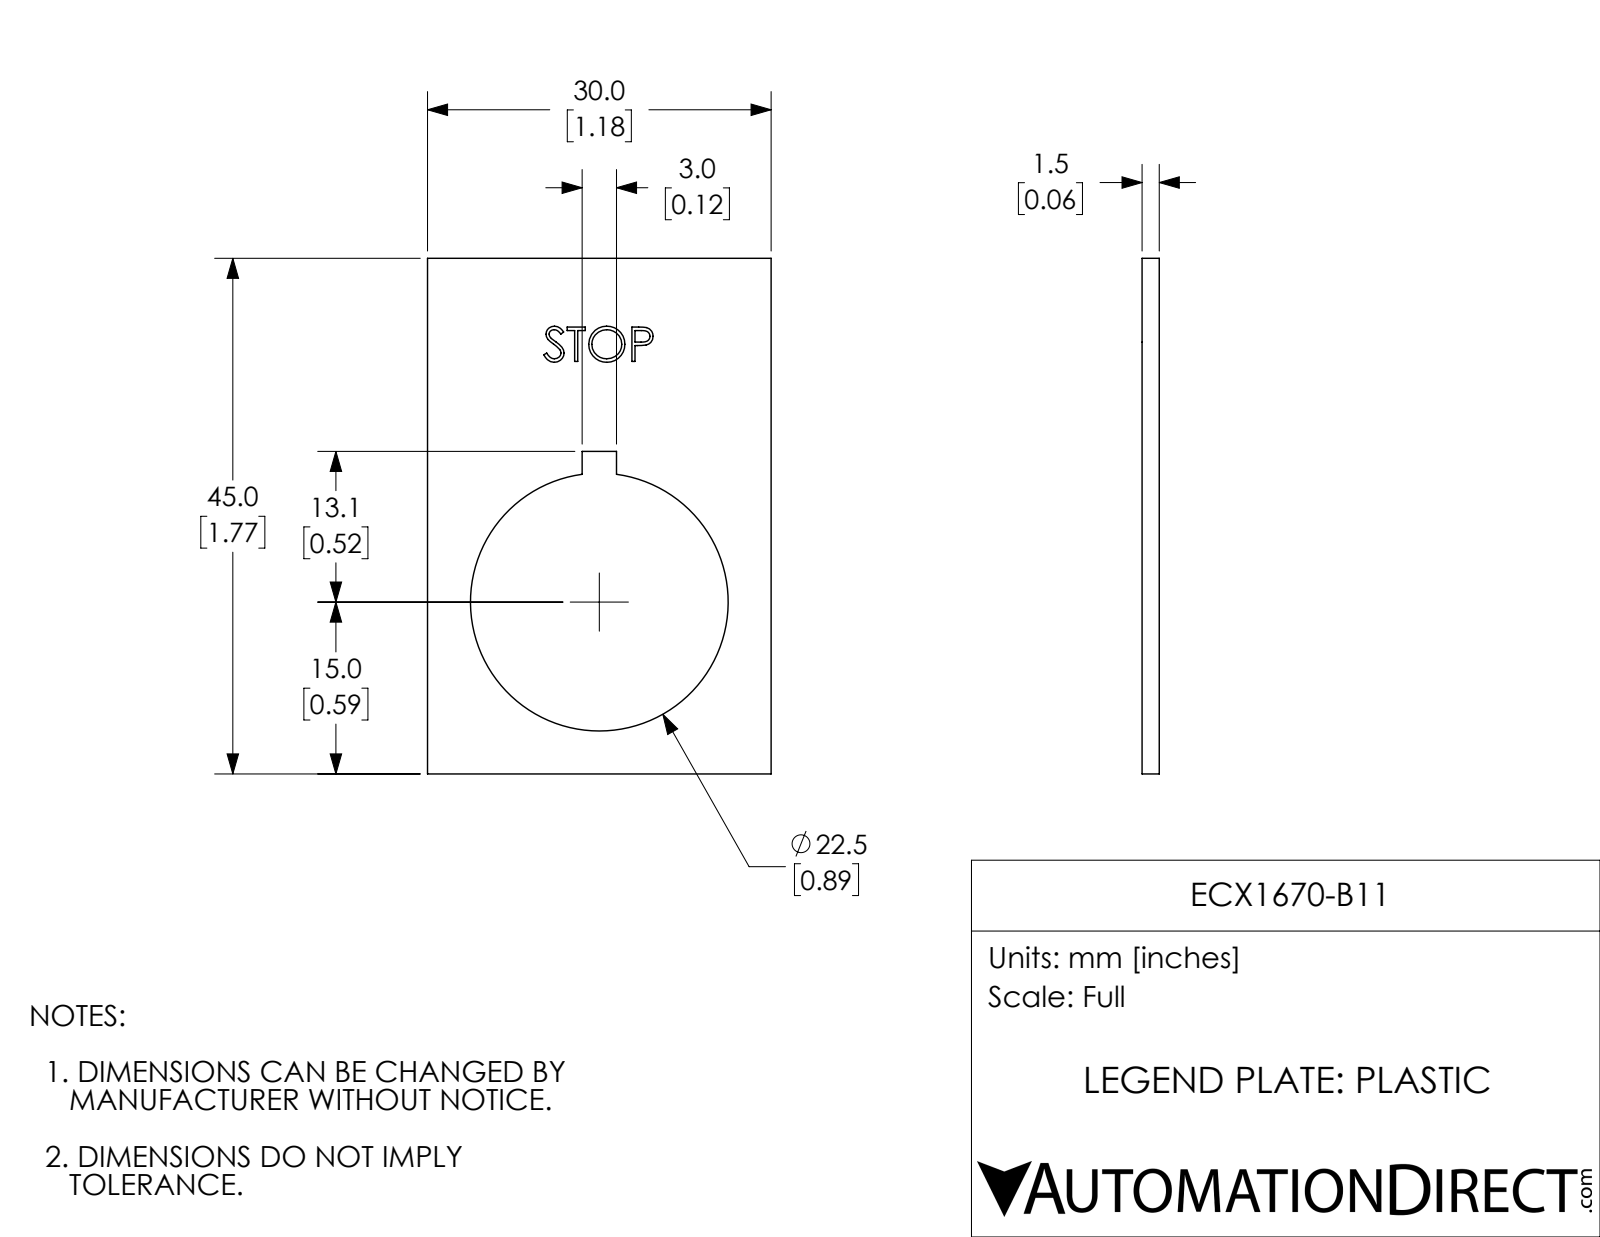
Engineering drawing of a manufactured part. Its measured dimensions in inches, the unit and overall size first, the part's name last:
Units: inches
Overall size (bounding box): 1.772 × 1.181 × 0.059
Round holes (diameter × count): ⌀0.886 ×1
Main face-to-face distances: 0.059, 1.181, 1.772, 0.058, 0.531, 0.65, 1.108, 0.663, 0.118, 0.197
Volume: 0.087 in³ · Surface area: 3.459 in²
Bodies: 1 solid, 65 faces (33 planar, 3 cylindrical, 29 other)
Part name (STEP PRODUCT): ECX1670-B11
STEP written by: SolidWorks 2017 (AUTOMOTIVE_DESIGN)
